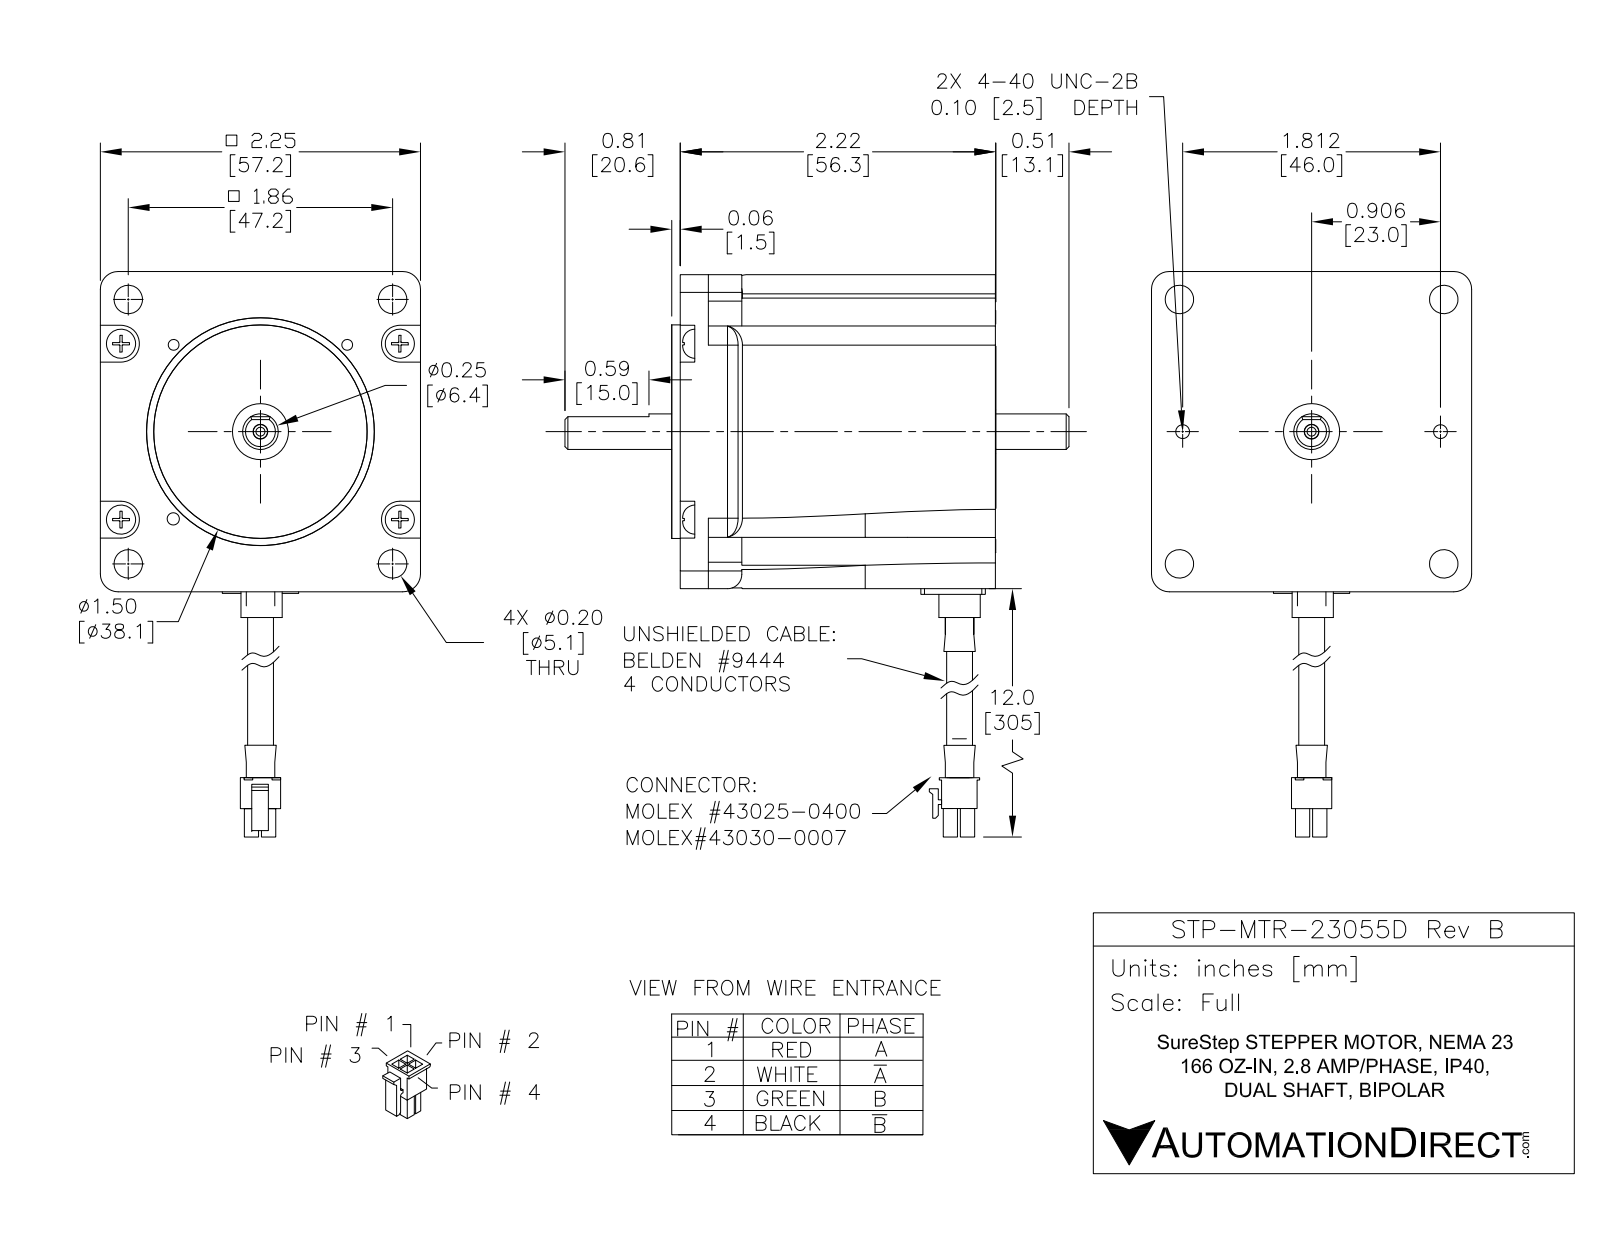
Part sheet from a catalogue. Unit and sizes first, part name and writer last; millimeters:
Units: millimetres
Overall size (bounding box): 368.9 × 90 × 56.1
Round holes (diameter × count): ⌀2.5 ×4, ⌀5.1 ×4, ⌀2.2 ×2, ⌀3.2 ×2, ⌀3.2 ×2, ⌀1.6 ×1, ⌀6.4 ×1, ⌀10 ×1, ⌀10.1 ×1, ⌀11.8 ×1, ⌀40.6 ×1, ⌀54.7 ×1
Round bosses / shafts (diameter × count): ⌀43.2 ×1, ⌀38.1 ×1, ⌀7.4 ×1, ⌀6.4 ×1, ⌀5.5 ×1
Partial cylindrical surfaces — rounded edges, fillets, slot ends (radius × count): R3.2 ×10, R0.6 ×4, R3.3 ×4, R4.4 ×4, R5 ×4, R0.3 ×3, R0.2 ×1, R2.5 ×1
Main face-to-face distances: 56.1, 8, 51.2, 43.2, 5.2, 13.2, 56.3, 5.1, 13.1, 56.3
Hole centre spacings: 8, 15.8, 29.4, 30, 33.4, 39.4, 41.9, 46.4
Volume: 149 700 mm³ · Surface area: 34 160 mm²
Bodies: 4 solids, 484 faces (325 planar, 110 cylindrical, 49 other)
Part name (STEP PRODUCT): STP-MTR-23055D
STEP written by: SolidWorks 2017 (AUTOMOTIVE_DESIGN)
